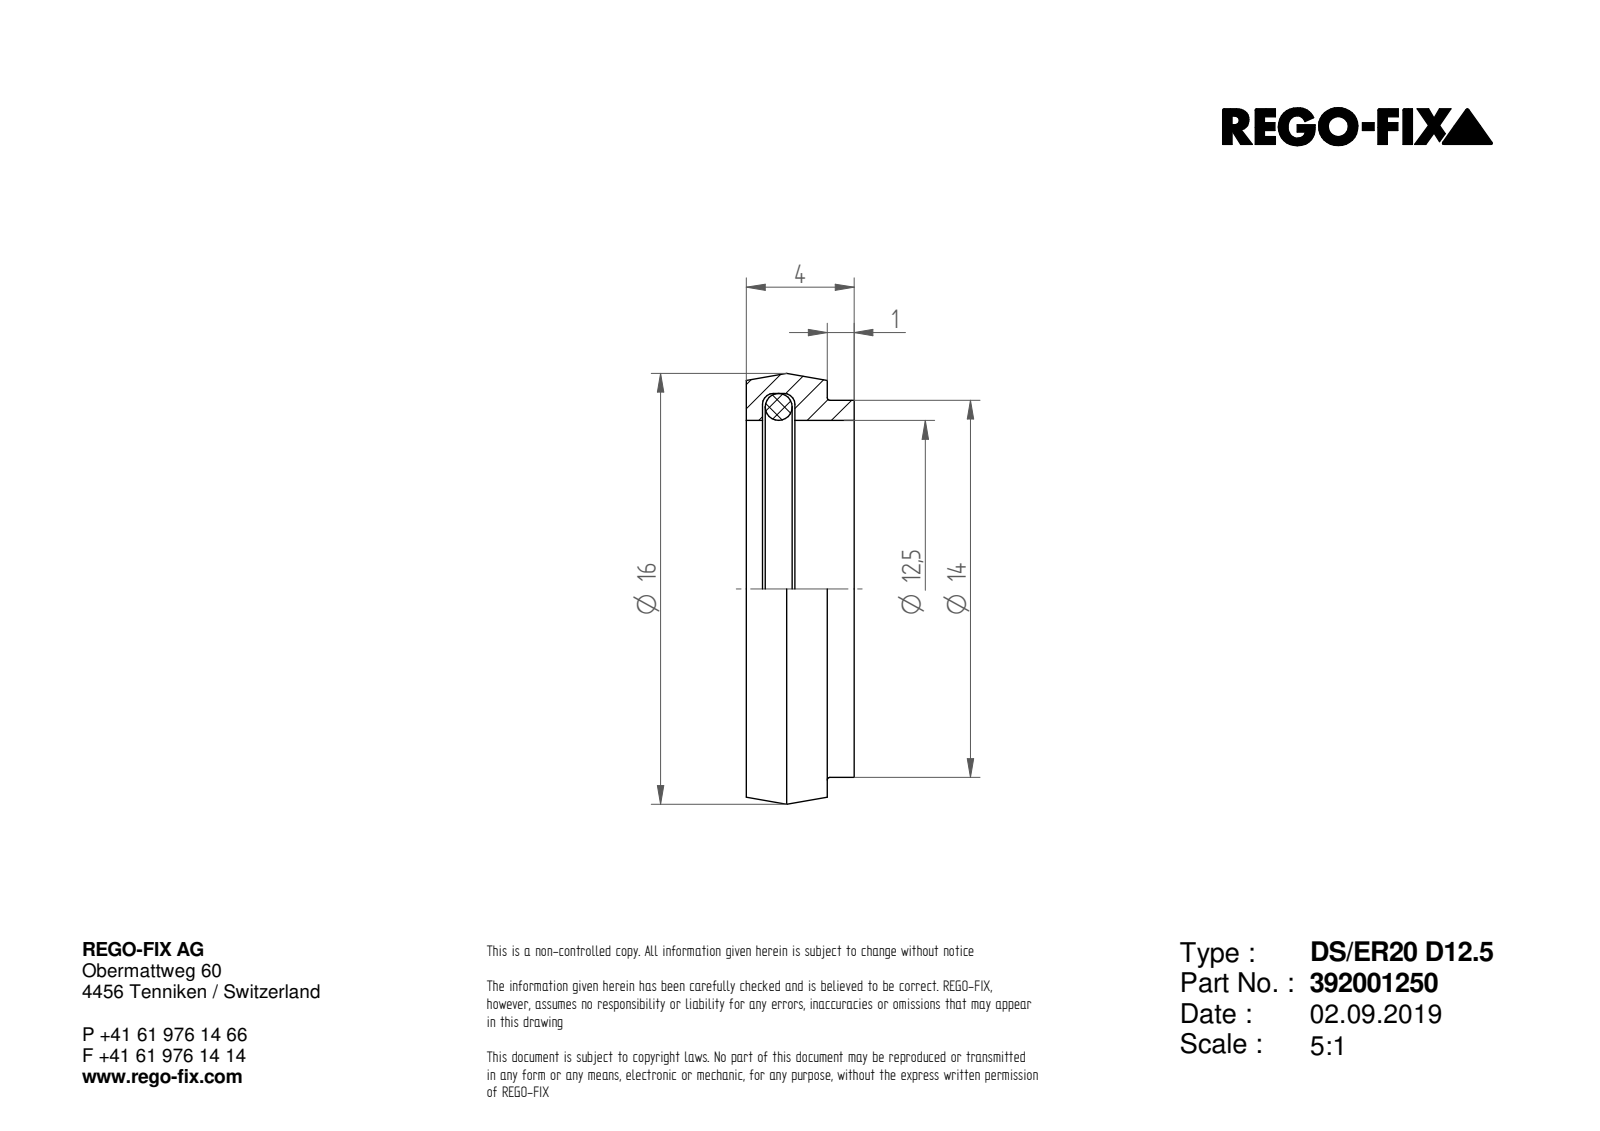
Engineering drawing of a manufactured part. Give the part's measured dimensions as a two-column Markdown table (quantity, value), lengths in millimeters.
| quantity | value |
| --- | --- |
| part name | NOCUT |
| STEP written by | SIEMENS PLM Software Solid Edge ST10 (AUTOMOTIVE_DESIGN) |
| units | millimeters |
| bodies | 1 solid, 7 faces (3 planar, 3 cylindrical, 1 other) |
| overall size | 16 × 16 × 4 |
| volume | 266 mm³ |
| surface area | 507 mm² |
| round holes (diameter × count) | 12.5 × 1 |
| round bosses / shafts (diameter × count) | 16 × 1, 14 × 1 |
| main face-to-face distances | 3, 1, 4 |
